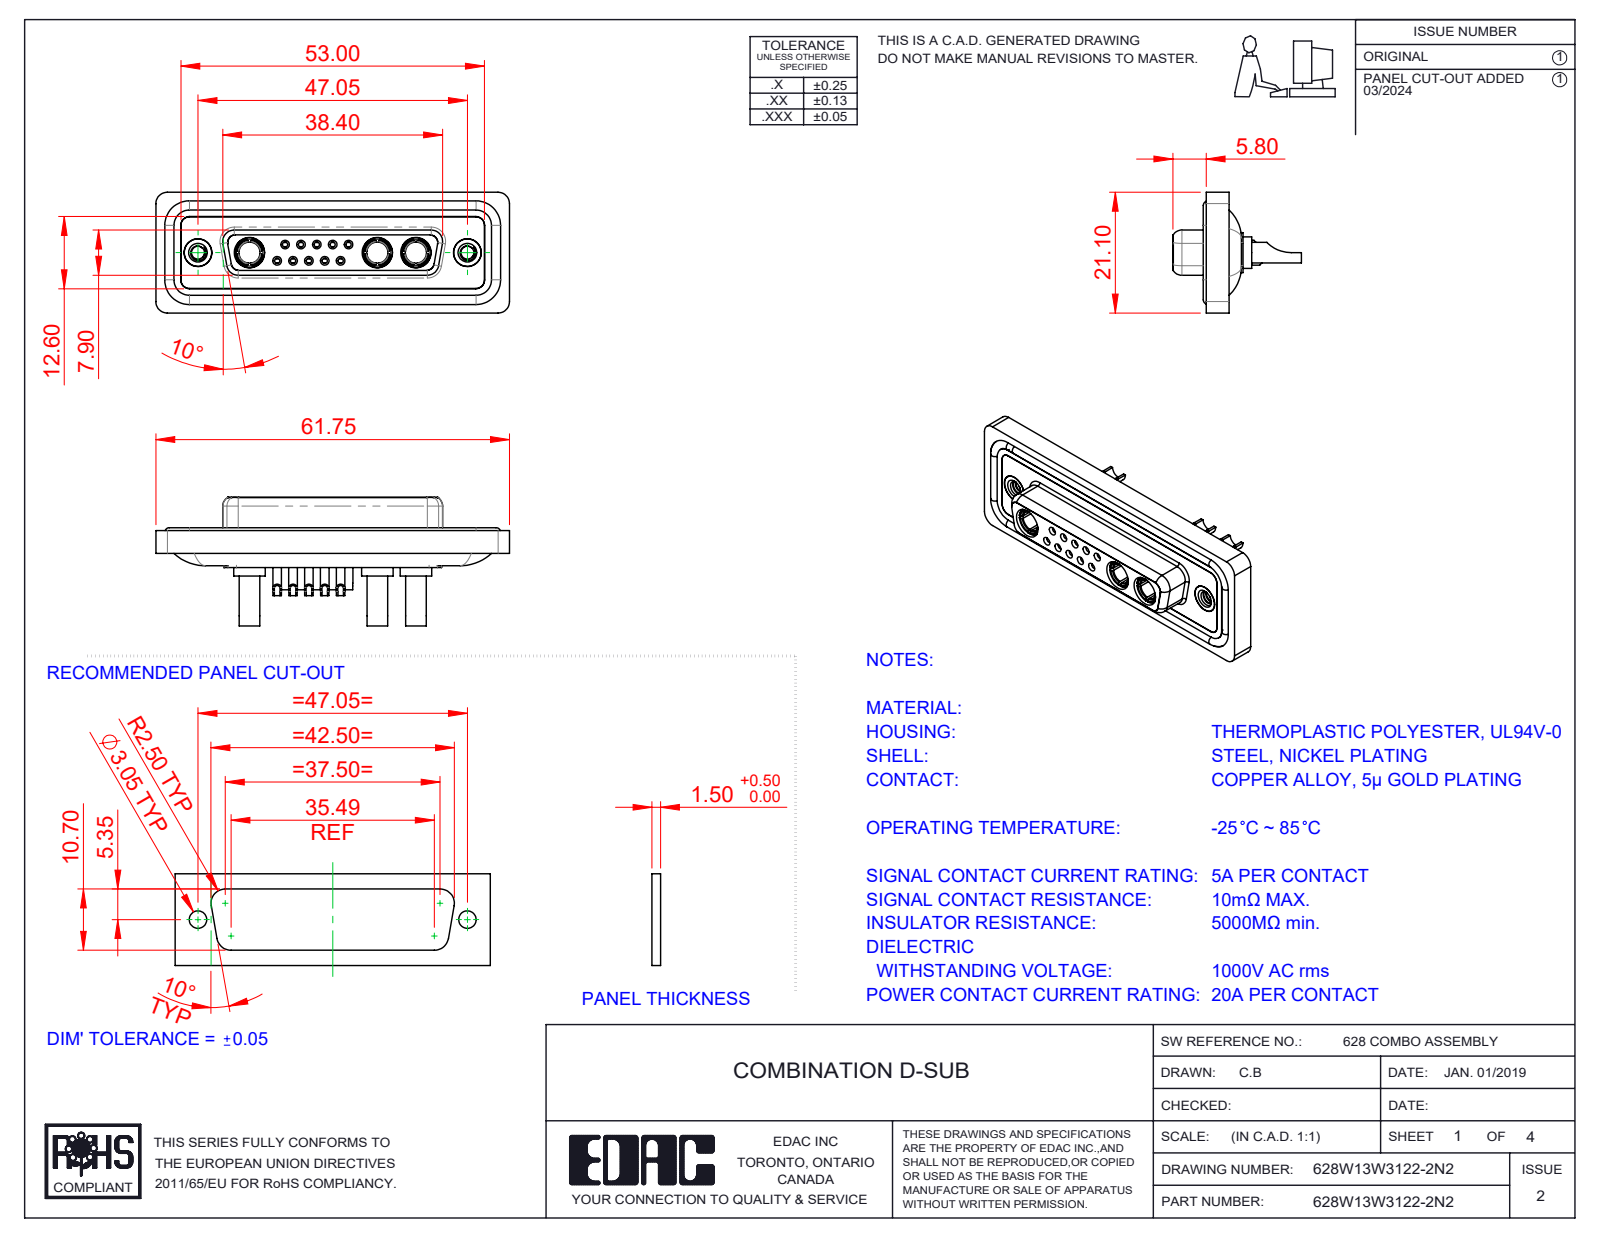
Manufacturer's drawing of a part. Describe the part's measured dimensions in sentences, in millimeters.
The part is named "628Combo Housing_13W3; 628Combo Shell Rear_25 Contacts; 628Combo Shell Front_25 Contacts; 628Combo Contact Row 2_22 (+5 more)". Its 3-D file was written by "SolidWorks 2023 (CONFIG_CONTROL_DESIGN)". It is 23 solids with 1176 faces: 371 planar, 476 cylindrical and 329 other. Overall it measures 61.75 by 22.45 by 21.1 millimeters. Its volume is 8 332 cubic millimeters and its surface area 14 061 square millimeters. Round holes: 10 of diameter 0.9, 10 of diameter 1, 10 of diameter 1.1, 10 of diameter 1.5, 10 of diameter 2, 5 of diameter 1.6, 5 of diameter 1.7, 5 of diameter 4.85, 3 of diameter 2.7, 3 of diameter 3.7, 3 of diameter 5.3, 2 of diameter 2.26. Round bosses or shafts: 10 of diameter 2.2, 9 of diameter 1.6, 3 of diameter 5.5, 3 of diameter 5.2, 3 of diameter 4.96, 3 of diameter 4.75, 3 of diameter 3.75, 3 of diameter 3.6. Partial cylindrical surfaces (rounded edges, fillets, slot ends): 22 of radius 1.5, 18 of radius 2, 8 of radius 1.35, 8 of radius 1.6, 6 of radius 1, 4 of radius 0.25, 4 of radius 0.5, 4 of radius 0.6. The main face-to-face distances are 0.4, 1.8, 7.45, 5.65, 0.5, 6.6, 7.05, 1.6, 2.9, 1.1. The hole center spacings are 3.16, 2.77, 5.03, 5.04, 5.54, 8.31, 7.49, 2.76.
